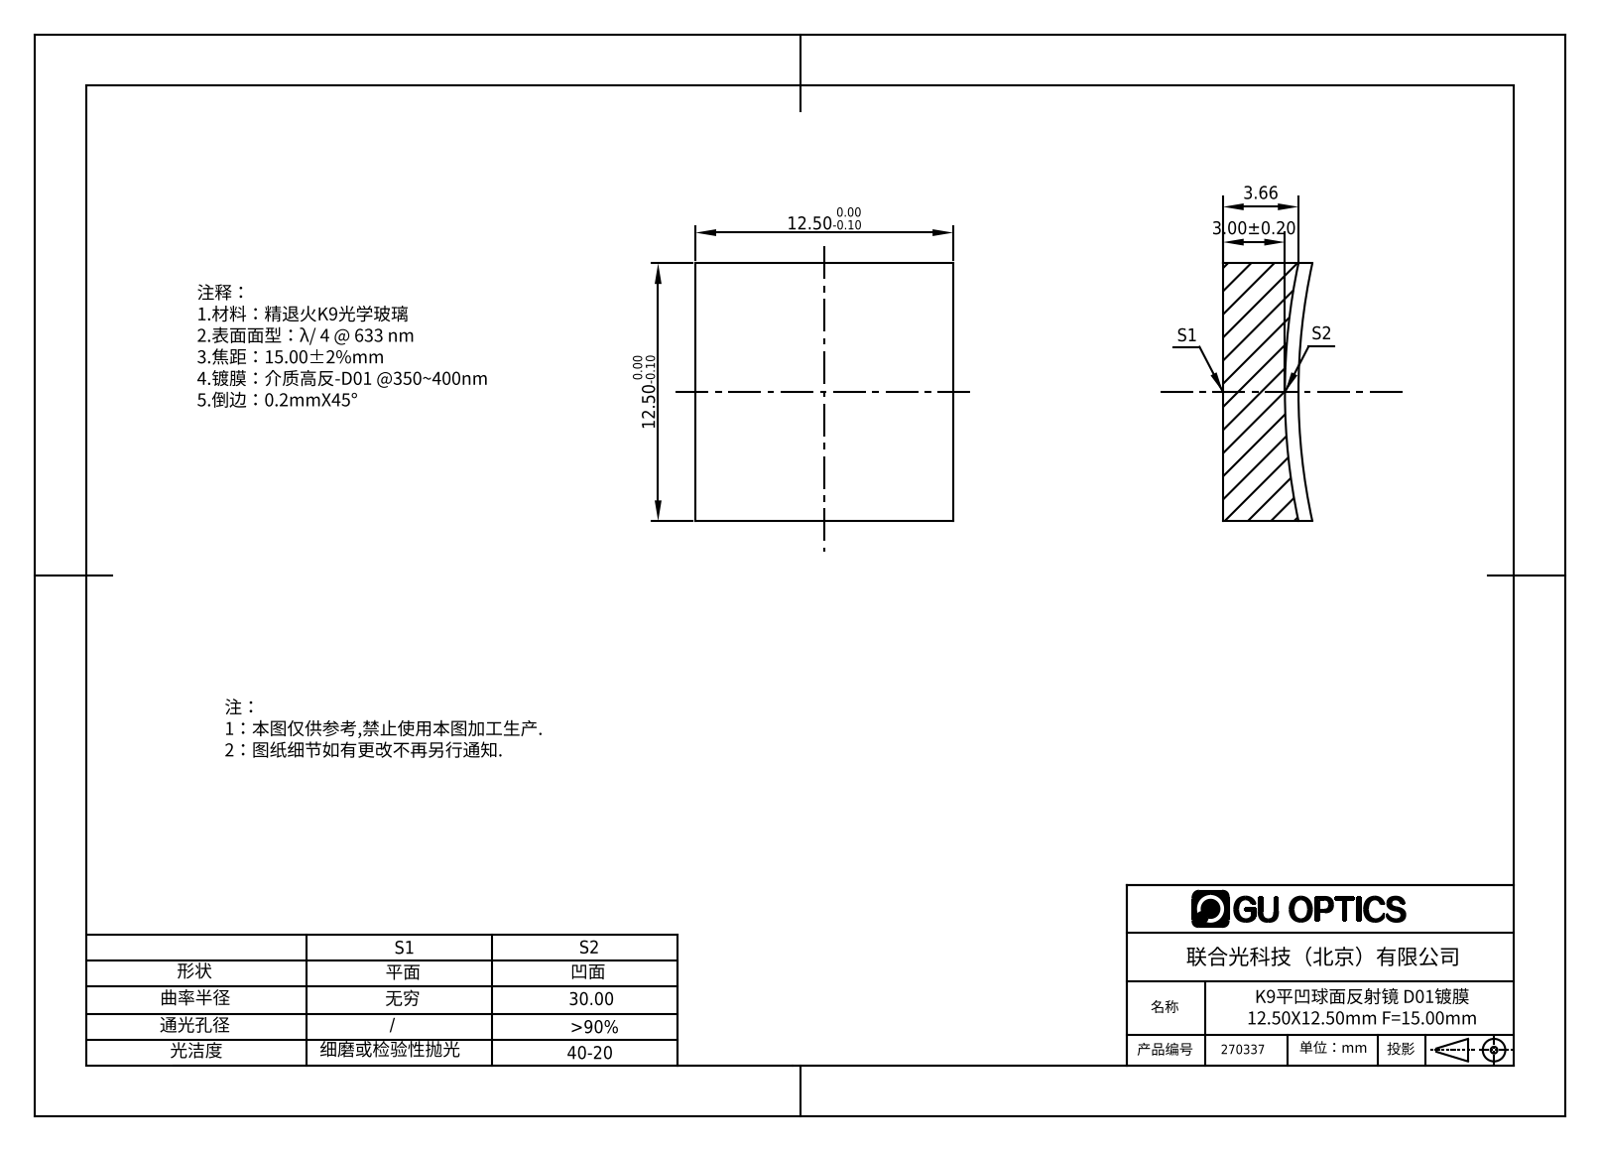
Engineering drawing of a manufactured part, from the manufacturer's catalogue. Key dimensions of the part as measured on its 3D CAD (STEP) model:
Part name (STEP PRODUCT): 270012
STEP written by: SolidWorks 2019 (AUTOMOTIVE_DESIGN)
Units: millimetres
Bodies: 1 solid, 7 faces (5 planar, 0 cylindrical, 2 other)
Overall size (bounding box): 12.5 × 12.5 × 4.33
Volume: 537 mm³ · Surface area: 509 mm²
Main face-to-face distances: 12.5
